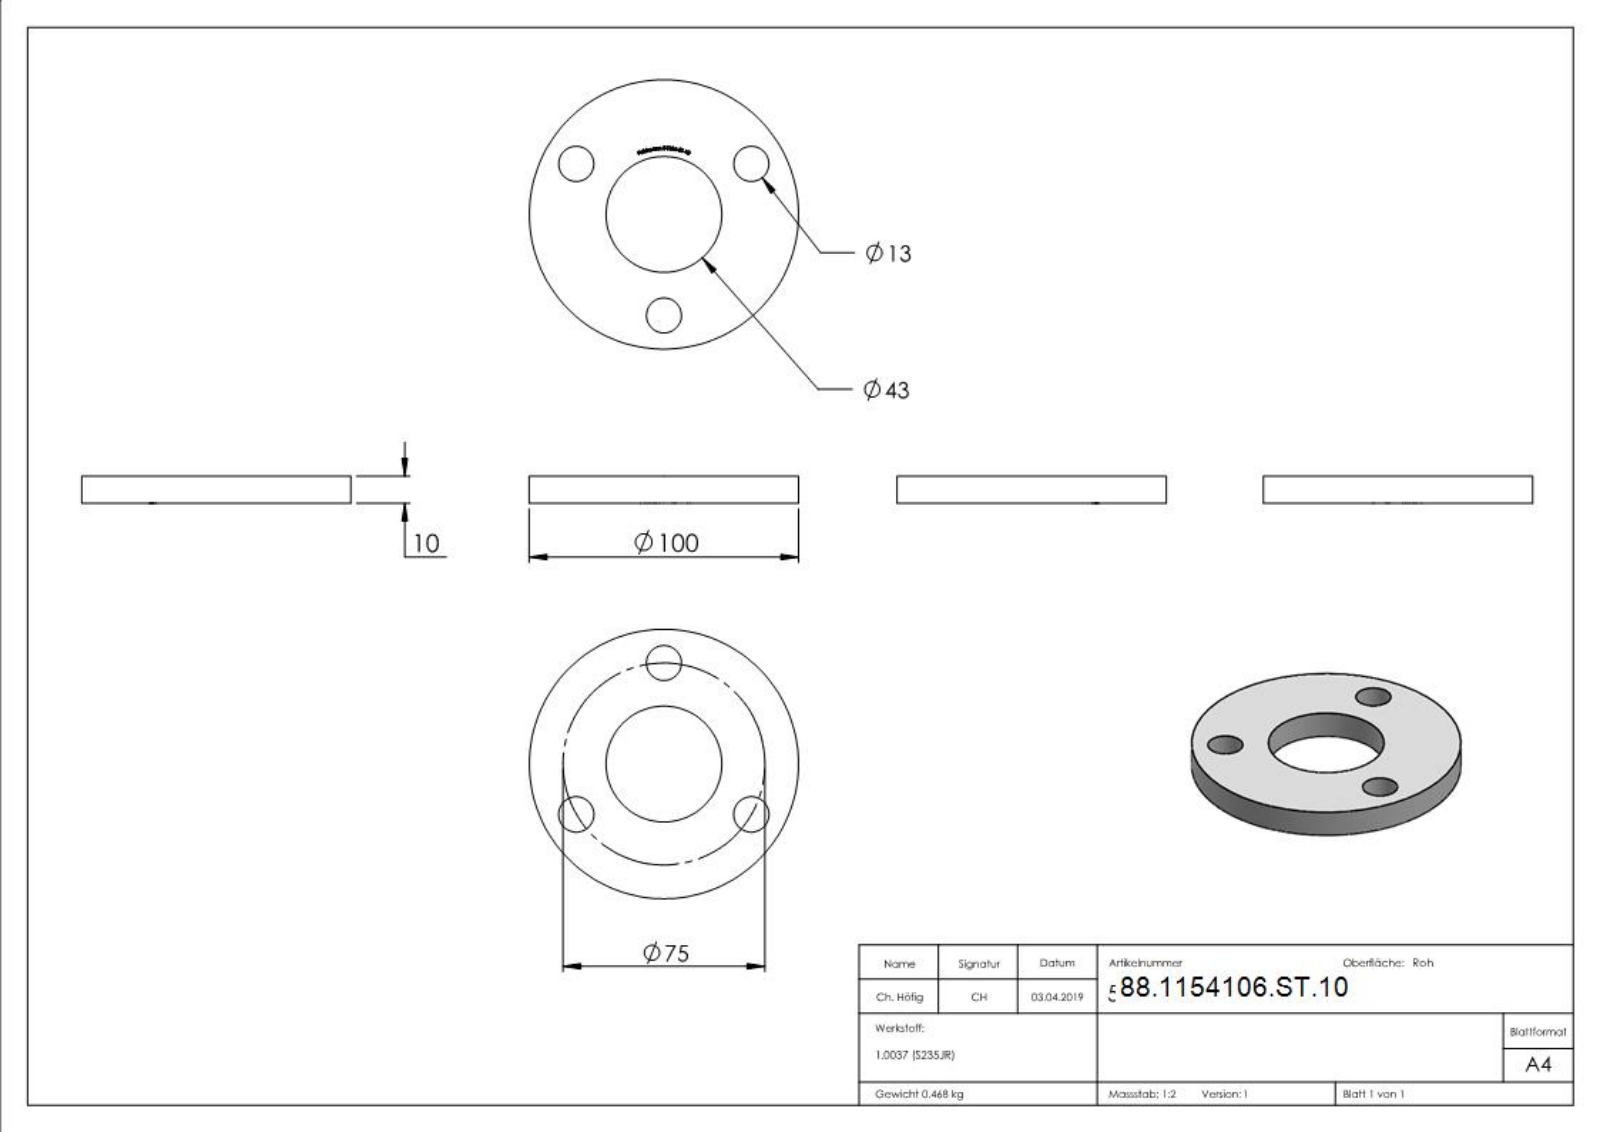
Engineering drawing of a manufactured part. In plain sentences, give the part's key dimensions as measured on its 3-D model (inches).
The part is named "54106-ST-10". Its 3-D file was written by "SolidWorks 2015 (CONFIG_CONTROL_DESIGN)". It is 1 solid with 242 faces: 134 planar, 10 cylindrical and 98 other. Overall it measures 3.937 by 3.937 by 0.394 inches. Its volume is 3.664 cubic inches and its surface area 27.49 square inches. Round holes: 3 of diameter 0.512, 1 of diameter 1.693. Round bosses or shafts: 1 of diameter 3.937. The main face-to-face distances are 0.394, 0.39, 0.028, 0.021, 0.026, 0.024, 0.026, 0.052, 0.057, 0.016. The hole center spacings are 1.476, 2.557, 2.557.
